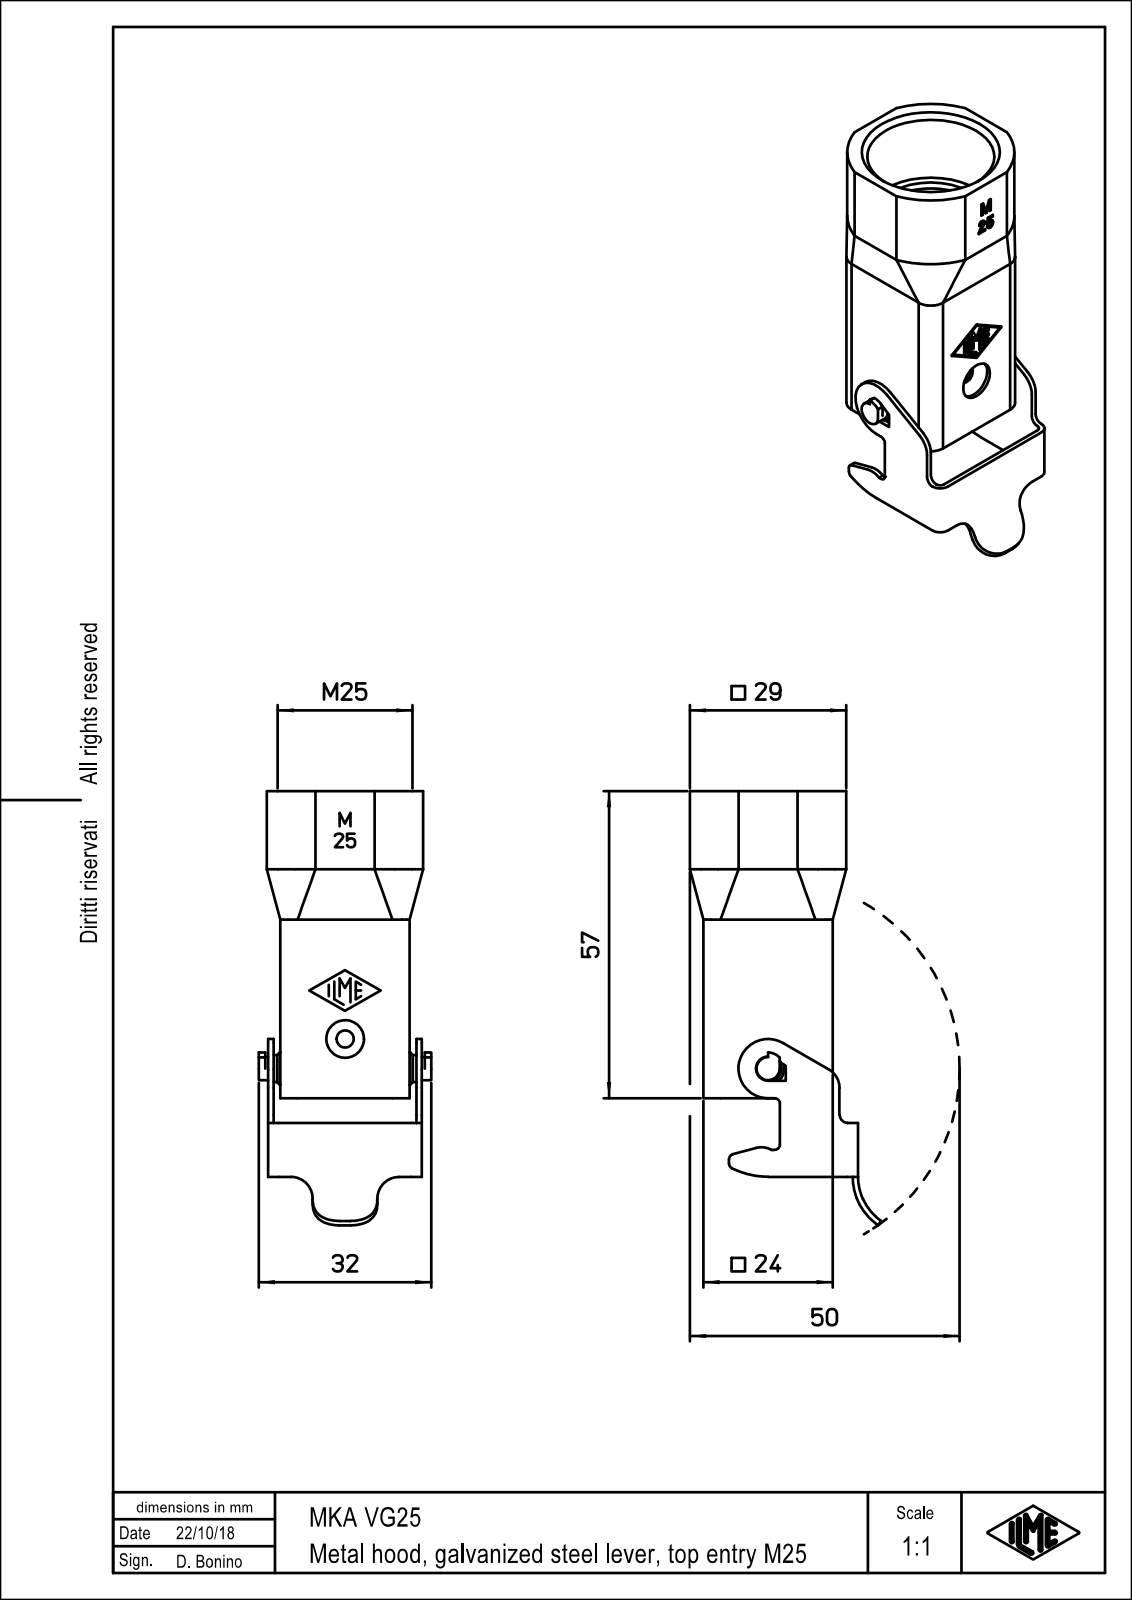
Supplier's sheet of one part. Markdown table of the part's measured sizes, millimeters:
| quantity | value |
| --- | --- |
| part name | MKA_VG25 |
| STEP written by | PTC Creo Elements/Direct Modeling 19.0B 21-Mar-2015 (C) Parametric Technology GmbH (AUTOMOTIVE_DESIGN) |
| units | millimeters |
| bodies | 1 solid, 306 faces (214 planar, 81 cylindrical, 11 other) |
| overall size | 80.6 × 35.75 × 32 |
| volume | 10 511 mm³ |
| surface area | 13 306 mm² |
| round holes (diameter × count) | 3.2 × 1, 7 × 1, 20 × 1, 25 × 1 |
| round bosses / shafts (diameter × count) | 6 × 1, 5 × 1, 4.3 × 1 |
| partial cylindrical surfaces (radius × count) | 0.25 × 15, 1 × 6, 2 × 6, 3.2 × 4, 4 × 4, 0.12 × 3, 5 × 2, 0.5 × 1 |
| main face-to-face distances | 1.2, 22.8, 26.5, 21.6, 24, 1.25, 1, 27.5, 3.7, 2.45 |
